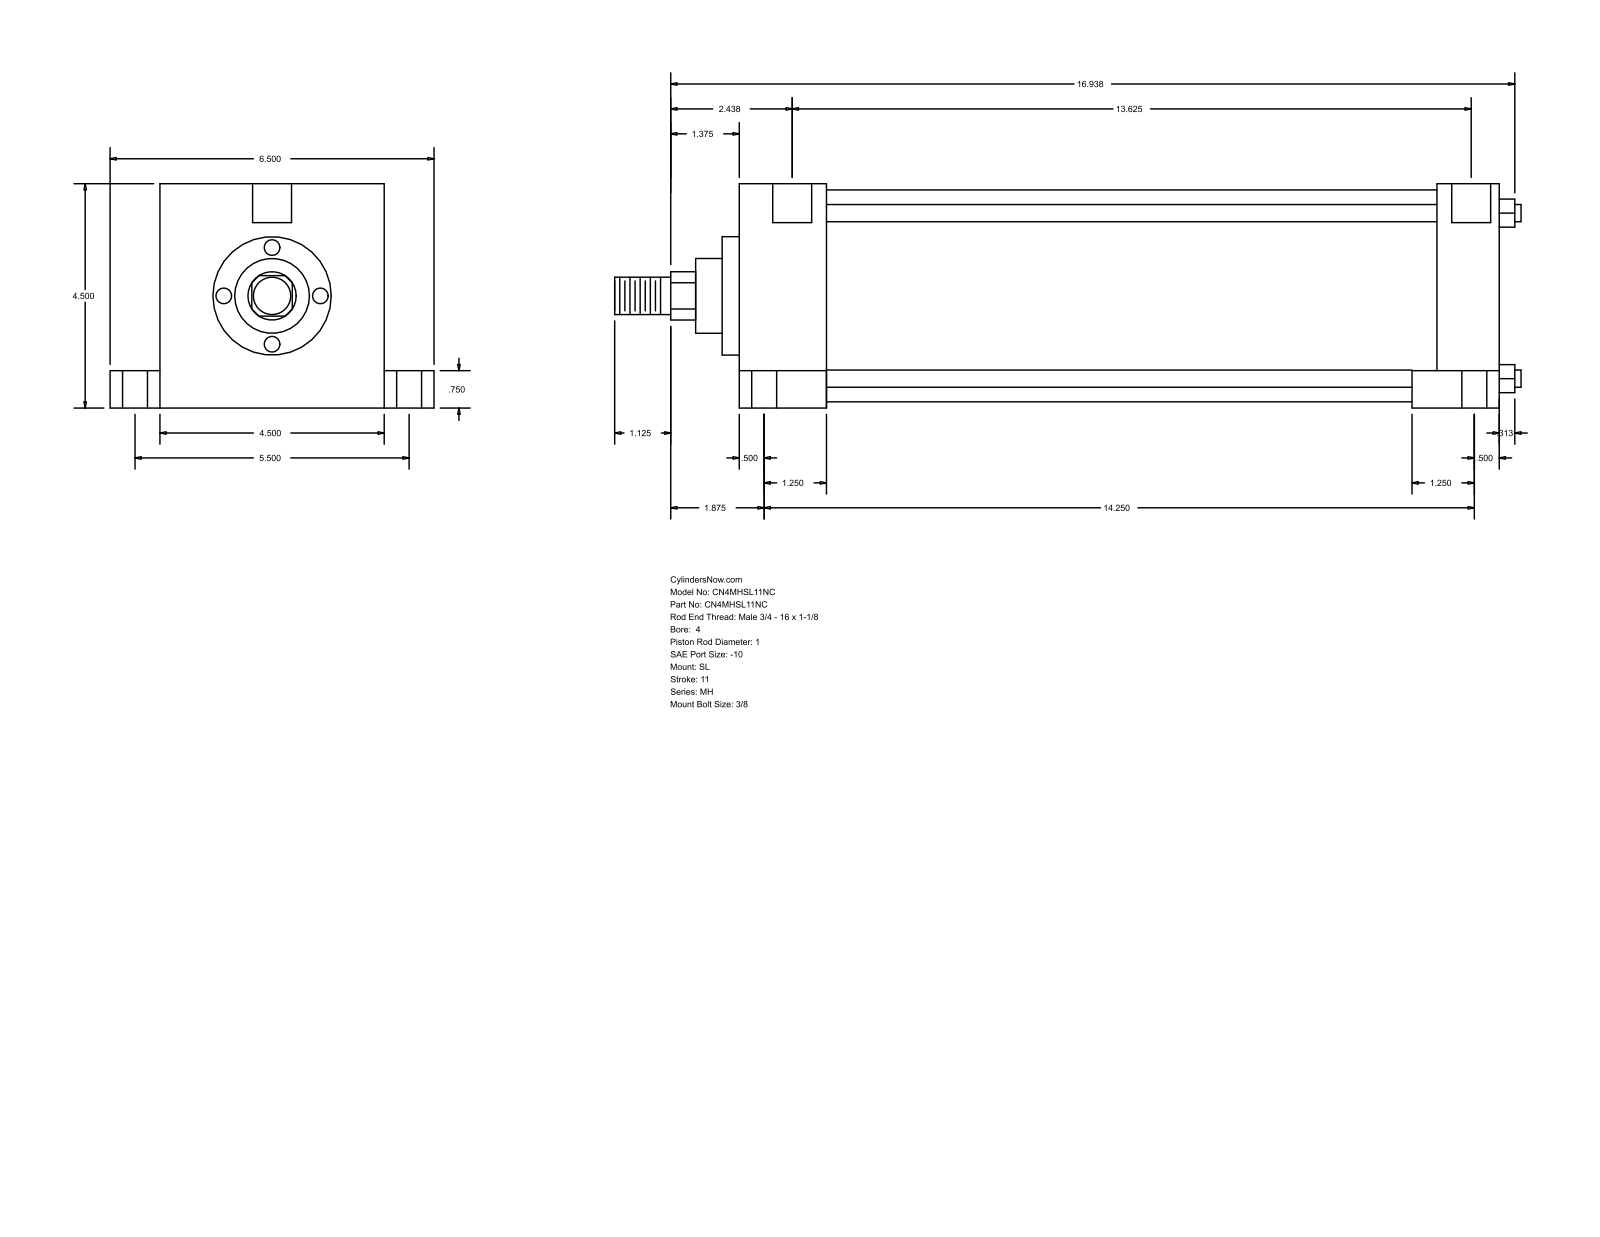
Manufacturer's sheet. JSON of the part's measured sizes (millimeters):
{"part_name": "MH_SL__0400_1", "step_written_by": "GSSL Pune (CONFIG_CONTROL_DESIGN)", "units": "millimeters", "bodies": {"solids": 0, "faces": 110, "planar": 77, "cylindrical": 33, "other": 0}, "overall_size": [461.96, 165.1, 114.3], "round_holes": [[8.73, 4], [12.7, 4], [19.05, 4], [19.84, 2]], "round_bosses_or_shafts": [[8.76, 4], [107.95, 1], [60.33, 1], [38.1, 1], [25.4, 1], [19.05, 1]], "partial_cylinders_radius": [[12.29, 1]], "face_to_face_distances": [114.3, 387.35, 44.46, 342.89, 355.6, 311.14, 31.75, 25.4, 139.7, 19.05], "hole_center_spacings": [1.58, 69.85, 69.87, 71, 71.3, 139.7, 347.66, 349.24]}
